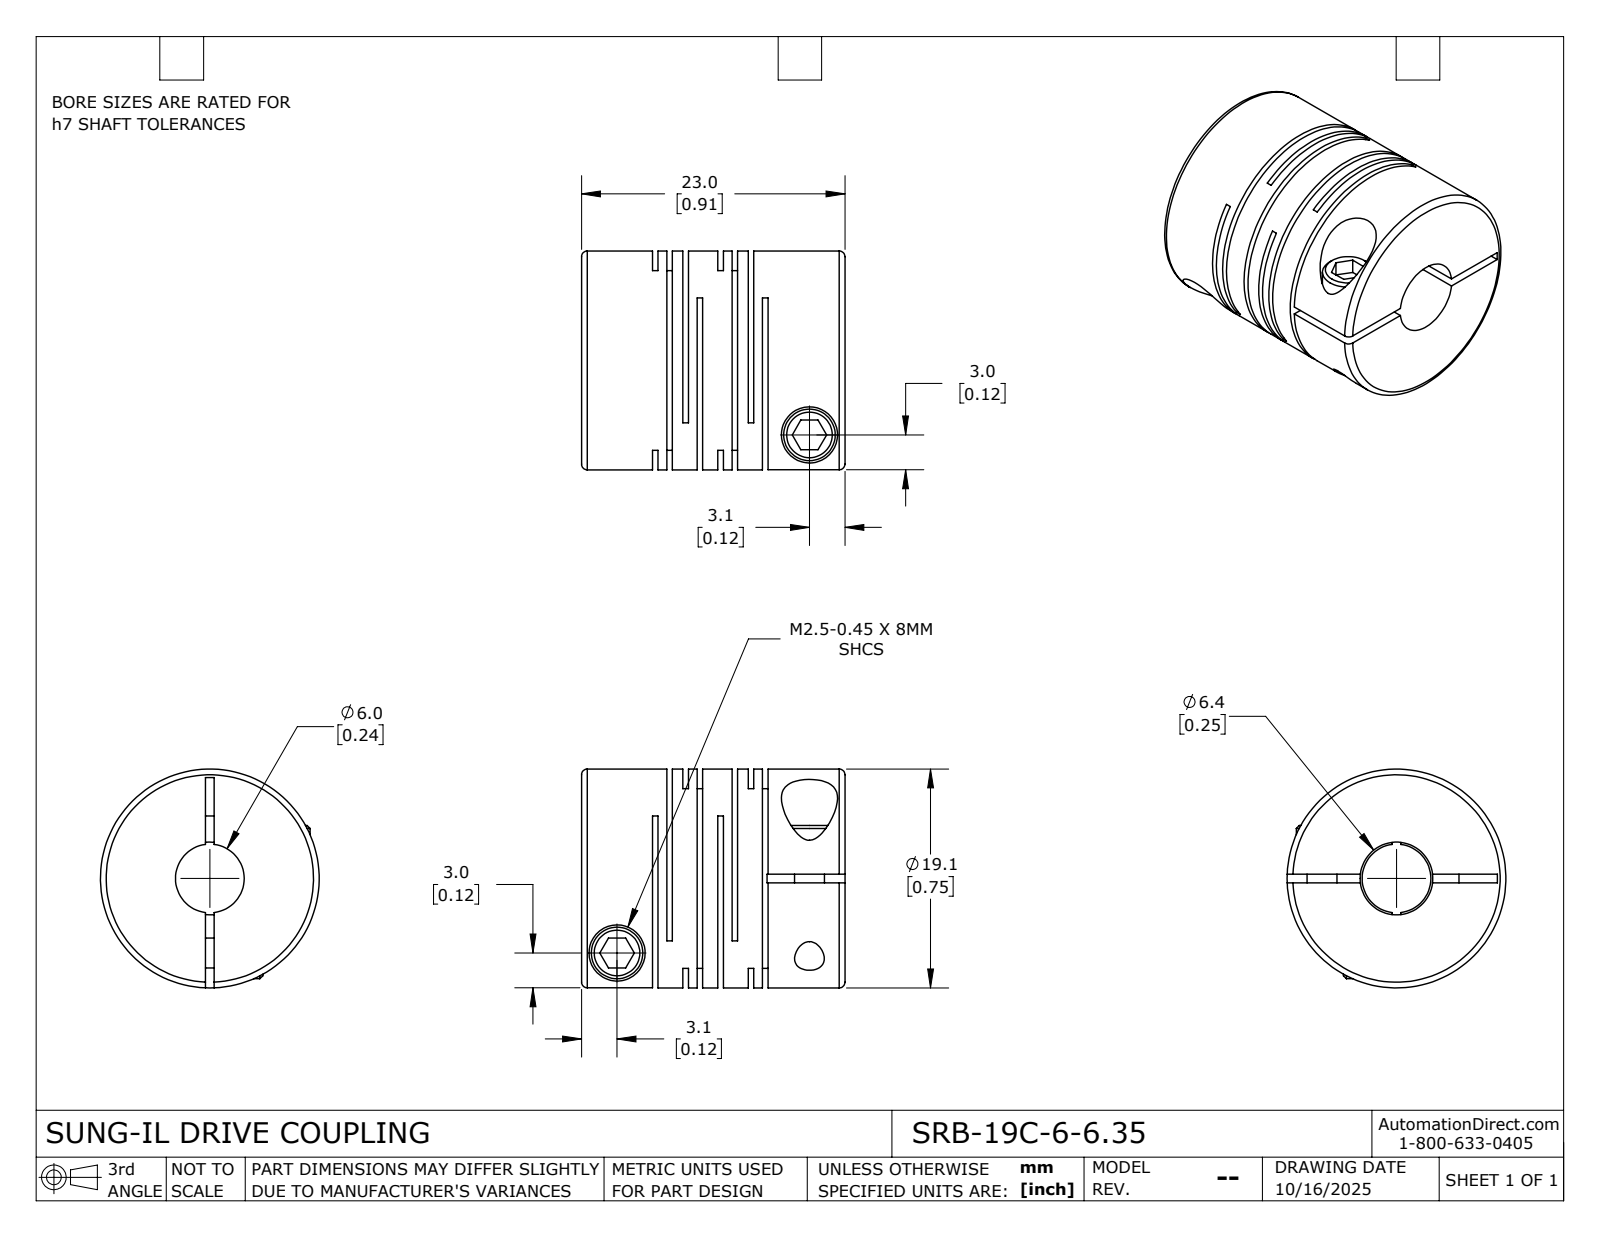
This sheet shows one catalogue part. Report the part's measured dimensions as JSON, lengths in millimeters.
{"part_name": "SRB-19C-6-6.35", "step_written_by": "SolidWorks 2024 (CONFIG_CONTROL_DESIGN)", "units": "millimeters", "bodies": {"solids": 1, "faces": 115, "planar": 60, "cylindrical": 42, "other": 13}, "overall_size": [23, 19.1, 19.1], "volume_mm3": 4836, "surface_area_mm2": 5970, "round_holes": [[2.6, 2], [4.9, 2], [6, 1], [6.35, 1]], "round_bosses_or_shafts": [[4.5, 2], [19.1, 1]], "face_to_face_distances": [2.65, 0.48, 1.25, 5.7, 2.17, 3.05, 5.22, 0.77, 4.45, 1.4]}
